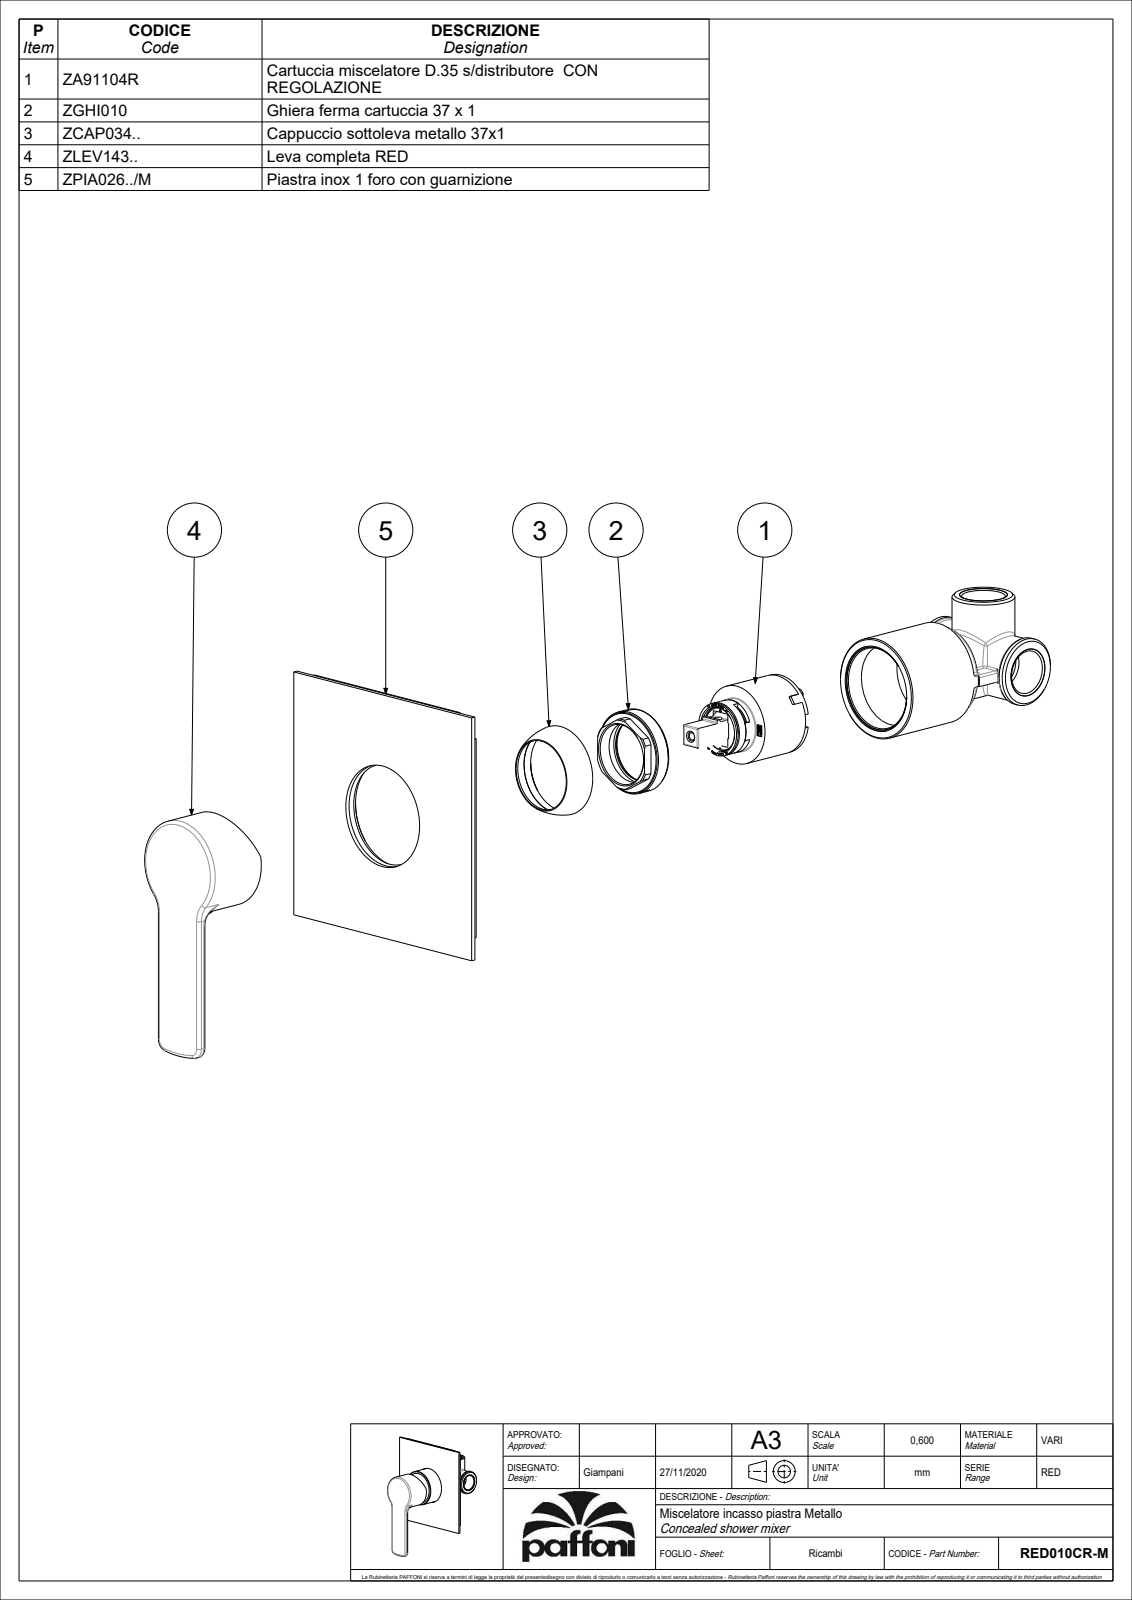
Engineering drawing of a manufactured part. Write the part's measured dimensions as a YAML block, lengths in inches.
part_name: "RED010CR-M"
step_written_by: "CREO PARAMETRIC BY PTC INC, 2020044 (CONFIG_CONTROL_DESIGN)"
units: inches
bodies: {solids: 2, faces: 970, planar: 559, cylindrical: 228, other: 183}
overall_size: [5.512, 4.331, 2.316]
volume: 4.224
surface_area: 88.52
round_holes:
  - {diameter: 0.13, count: 2}
  - {diameter: 0.157, count: 2}
  - {diameter: 0.118, count: 1}
  - {diameter: 0.177, count: 1}
  - {diameter: 0.197, count: 1}
  - {diameter: 0.768, count: 1}
  - {diameter: 0.783, count: 1}
  - {diameter: 1.055, count: 1}
  - {diameter: 1.142, count: 1}
  - {diameter: 1.22, count: 1}
  - {diameter: 1.276, count: 1}
  - {diameter: 1.417, count: 1}
round_bosses_or_shafts:
  - {diameter: 1.764, count: 1}
  - {diameter: 1.693, count: 1}
  - {diameter: 1.378, count: 1}
  - {diameter: 0.925, count: 1}
  - {diameter: 0.921, count: 1}
  - {diameter: 0.858, count: 1}
  - {diameter: 0.299, count: 1}
  - {diameter: 0.217, count: 1}
partial_cylinders:
  - {radius: 0.02, count: 45}
  - {radius: 0.006, count: 11}
  - {radius: 0.012, count: 4}
  - {radius: 0.059, count: 4}
  - {radius: 0.039, count: 2}
  - {radius: 0.197, count: 2}
  - {radius: 0.394, count: 2}
  - {radius: 0.276, count: 1}
face_to_face_distances: [0.079, 2.13, 2.051, 0.177, 2.307, 2.228, 0.217, 1.988, 2.343, 0.65]
hole_center_spacings: [0.492]
